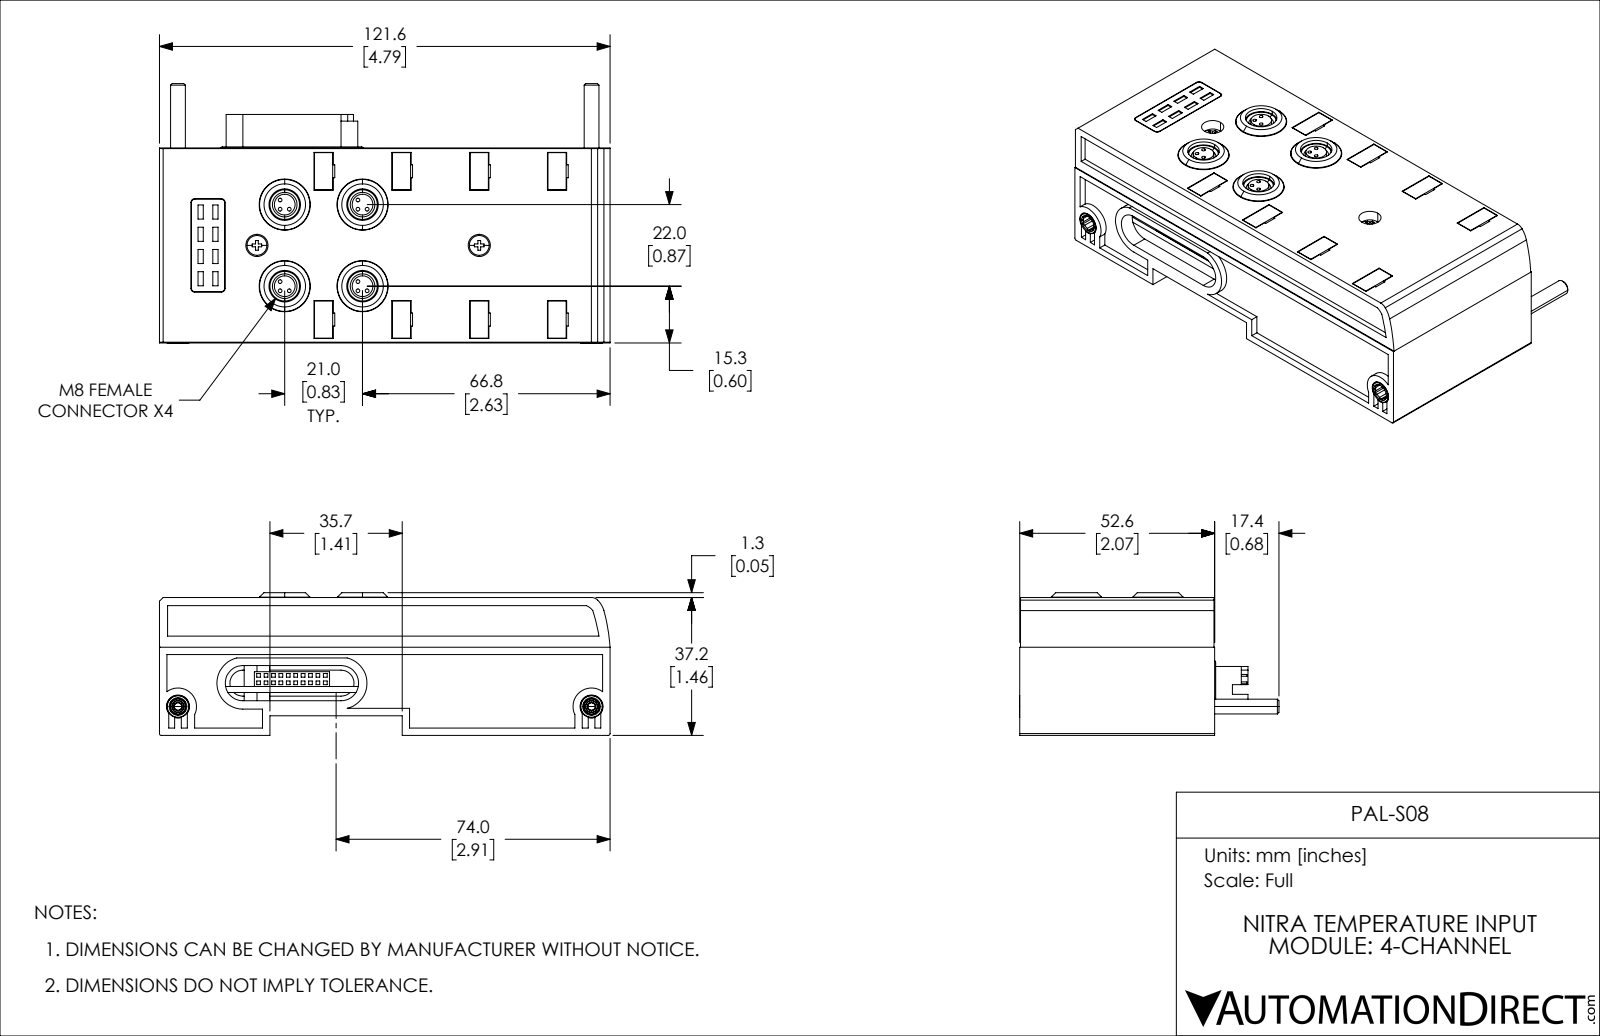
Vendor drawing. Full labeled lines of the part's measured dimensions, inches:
Part name (STEP PRODUCT): PAL-S08
STEP written by: SolidWorks 2019 (CONFIG_CONTROL_DESIGN)
Units: inches
Bodies: 5 solids, 898 faces (644 planar, 160 cylindrical, 94 other)
Overall size (bounding box): 4.787 × 2.756 × 1.516
Volume: 8.875 in³ · Surface area: 97.24 in²
Round holes (diameter × count): ⌀0.039 ×12, ⌀0.262 ×4, ⌀0.335 ×4, ⌀0.543 ×4, ⌀0.128 ×2, ⌀0.236 ×2, ⌀0.244 ×2
Round bosses / shafts (diameter × count): ⌀0.535 ×4, ⌀0.22 ×4, ⌀0.272 ×2, ⌀0.236 ×2, ⌀0.211 ×2, ⌀0.157 ×2
Partial cylindrical surfaces — rounded edges, fillets, slot ends (radius × count): R0.039 ×8, R0.02 ×2, R0.034 ×2, R0.079 ×2, R0.082 ×2, R0.138 ×2, R0.177 ×2, R0.187 ×2
Main face-to-face distances: 0.528, 0.315, 0.063, 0.52, 0.937, 1.465, 0.622, 1.15, 0.417, 0.205
Hole centre spacings: 0.069, 0.098, 0.827, 0.866, 1.197, 0.78, 0.819, 0.877
